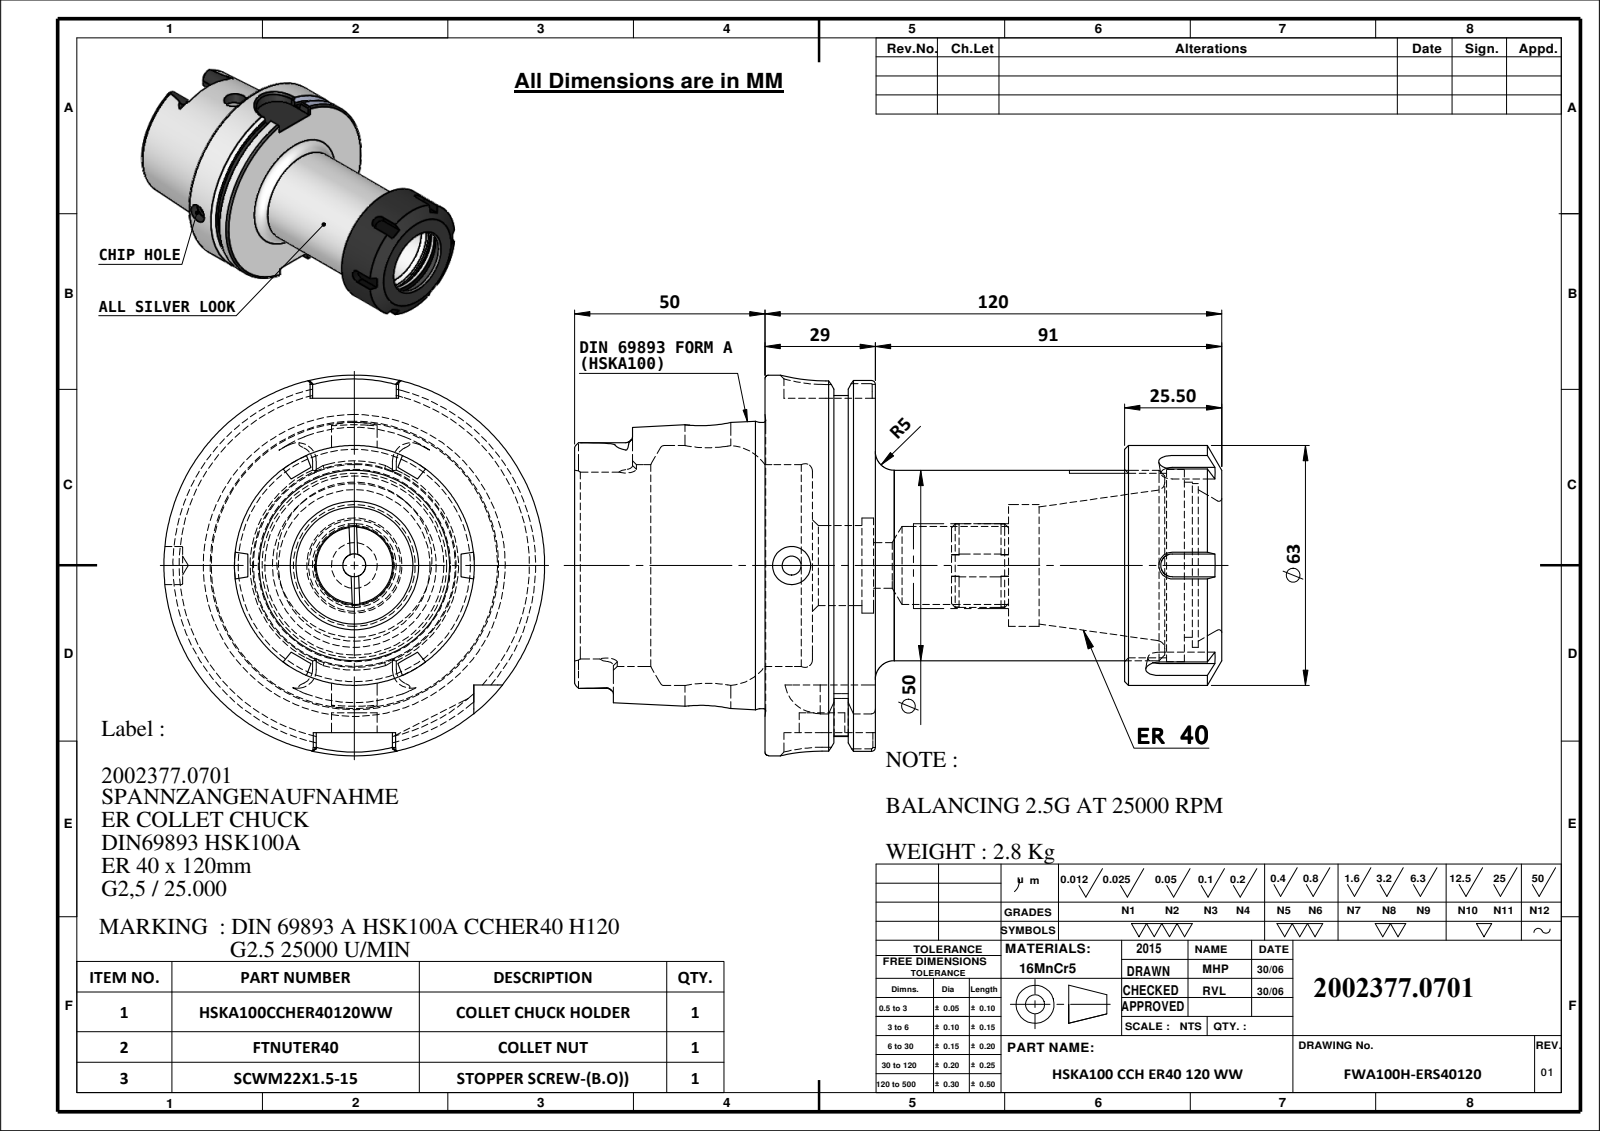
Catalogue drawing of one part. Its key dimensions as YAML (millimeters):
part_name: "SCWM22X1.5-15; HSKA100CCHER40120WW; Part1^HSKA100CCHER40120WW; Part2^HSKA100CCHER40120WW (+2 more)"
step_written_by: "SolidWorks 2018 (CONFIG_CONTROL_DESIGN)"
units: millimeters
bodies: {solids: 3, faces: 255, planar: 95, cylindrical: 66, other: 94}
overall_size: [170, 100, 100]
volume: 393667
surface_area: 82410
round_holes:
  - {diameter: 12, count: 3}
  - {diameter: 6, count: 1}
  - {diameter: 10, count: 1}
  - {diameter: 20.5, count: 1}
  - {diameter: 21, count: 1}
  - {diameter: 25, count: 1}
  - {diameter: 32, count: 1}
  - {diameter: 40.75, count: 1}
  - {diameter: 43, count: 1}
  - {diameter: 48.5, count: 1}
  - {diameter: 50.5, count: 1}
  - {diameter: 53, count: 1}
round_bosses_or_shafts:
  - {diameter: 100, count: 1}
  - {diameter: 92, count: 1}
  - {diameter: 75.16, count: 1}
  - {diameter: 50, count: 1}
  - {diameter: 22, count: 1}
partial_cylinders:
  - {radius: 1.8, count: 6}
  - {radius: 4.88, count: 4}
  - {radius: 10, count: 2}
  - {radius: 11, count: 1}
face_to_face_distances: [29, 12.5, 16.5, 56, 25.5, 94.5, 120, 107.5, 91, 82]
hole_center_spacings: [1.5, 30]
